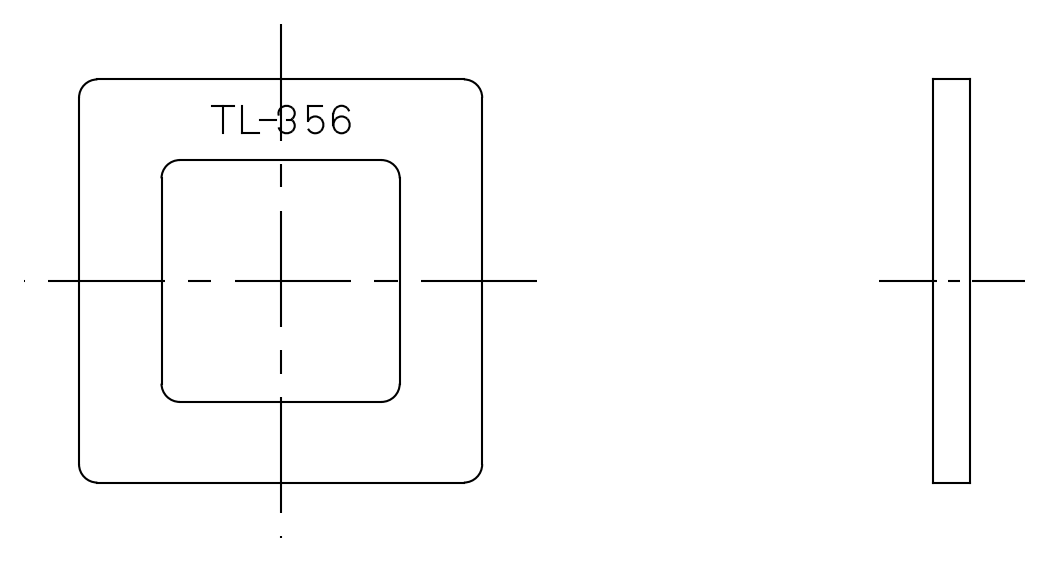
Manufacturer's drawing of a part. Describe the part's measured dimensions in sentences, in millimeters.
The part is named "67109598". Its 3-D file was written by "CADfix (AUTOMOTIVE_DESIGN)". It is 1 solid with 18 faces: 0 planar, 0 cylindrical and 18 other. Overall it measures 22 by 22 by 2 millimeters. Its volume is 625 cubic millimeters and its surface area 899 square millimeters.
